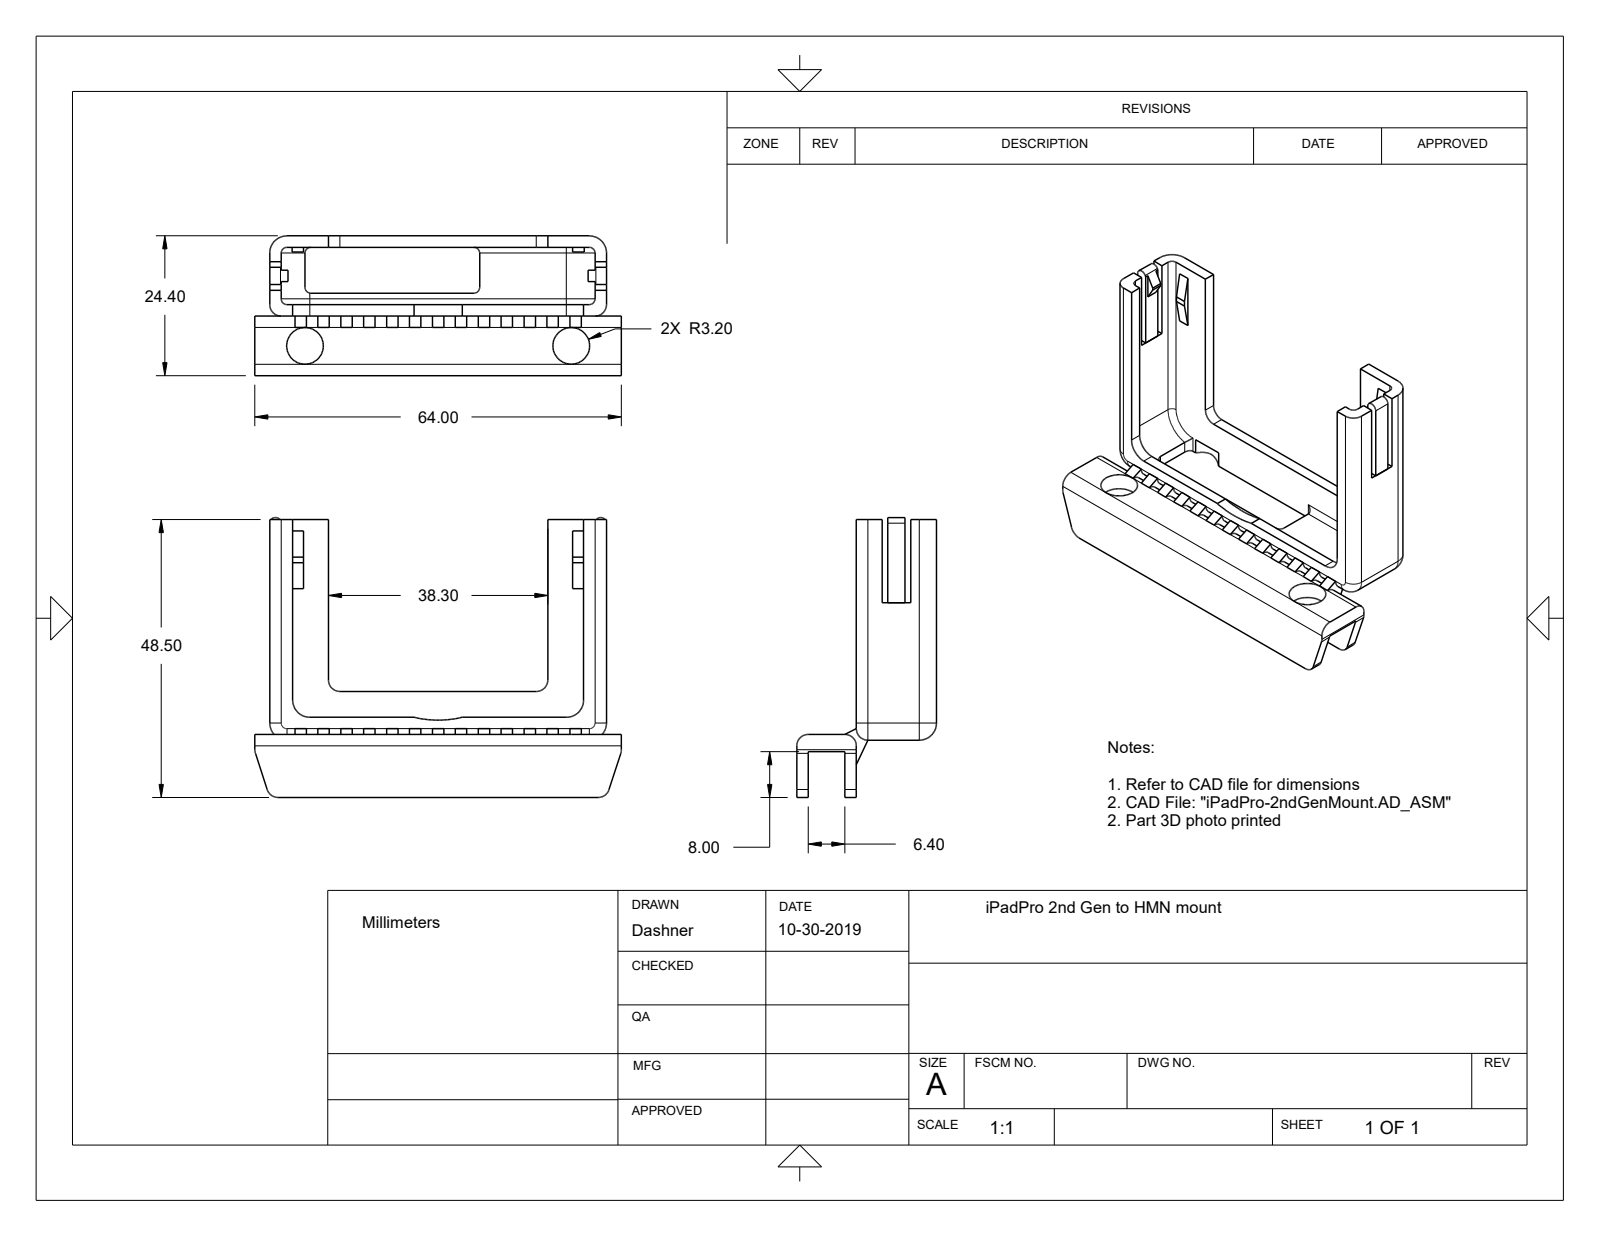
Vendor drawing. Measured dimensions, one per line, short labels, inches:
name: HMN_SnapTray; iPadPro-2ndGen_Saddle; SNAP_8x3x1mm; iPadPro-2ndGenMount
written by: Alibre (CONFIG_CONTROL_DESIGN)
unit: in
bodies: 4 solids, 203 faces (131 planar, 64 cylindrical, 8 other)
size: 2.52 × 1.924 × 0.961
volume: 0.536 in³; area: 14.91 in²
holes: 2× ⌀0.252
rounds: 12× R0.039, 11× R0.079, 7× R0.118, 2× R0.197, 1× R0.177, 1× R0.709
face distances: 0.079, 0.551, 0.882, 0.331, 0.472, 0.409, 0.157, 0.961, 0.118, 0.252
hole spacings: 1.841
